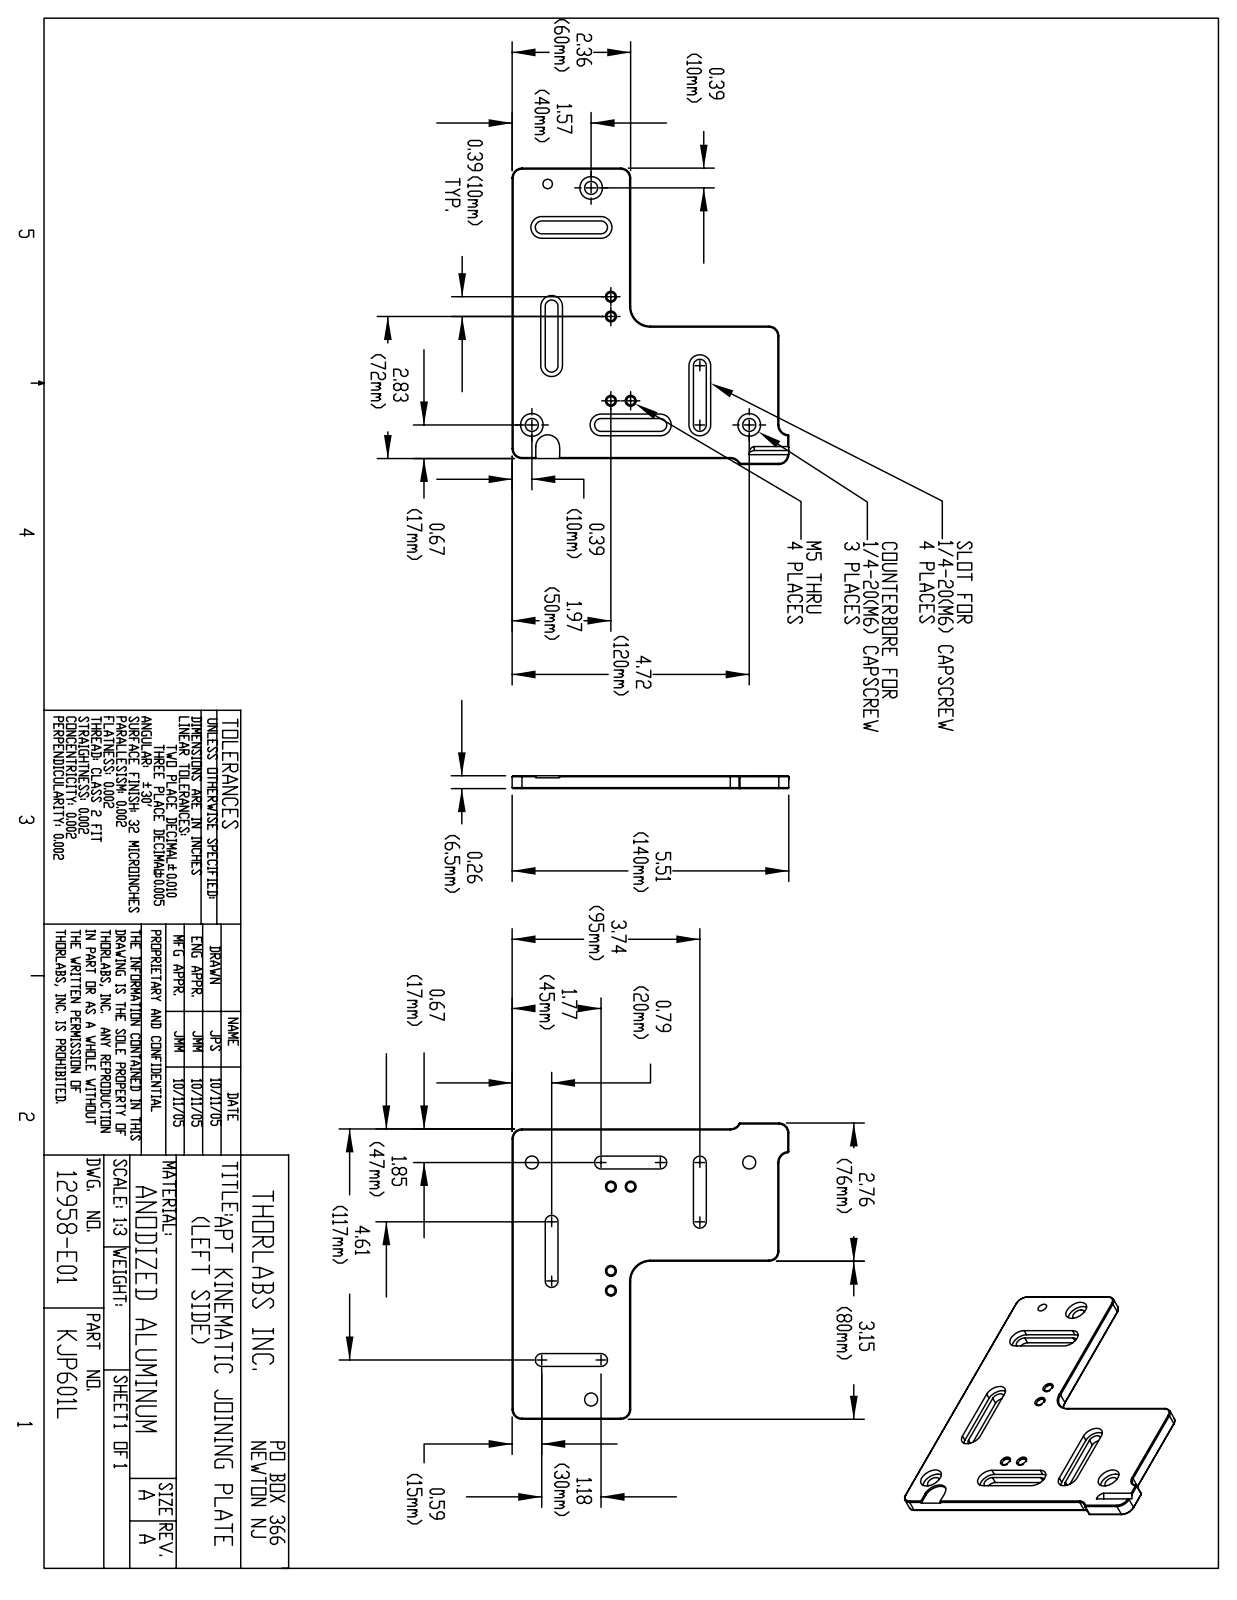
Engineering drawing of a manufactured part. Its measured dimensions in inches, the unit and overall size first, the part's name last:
Units: inches
Overall size (bounding box): 5.906 × 5.512 × 0.256
Round holes (diameter × count): ⌀0.165 ×4, ⌀0.26 ×3, ⌀0.453 ×3
Partial cylindrical surfaces — rounded edges, fillets, slot ends (radius × count): R0.02 ×18, R0.128 ×8, R0.217 ×8, R0.197 ×7, R0.098 ×1, R0.236 ×1, R0.394 ×1
Main face-to-face distances: 0.256, 0.118, 0.138, 0.089, 0.344, 2.953, 3.937, 0.433, 2.362, 2.638
Hole centre spacings: 0.394, 1.646, 1.681, 1.727, 2.026, 2.075, 2.112, 2.205
Bodies: 0 solids, 146 faces (38 planar, 70 cylindrical, 38 other)
Part name (STEP PRODUCT): 12958-E0W
STEP written by: SolidWorks 2007 (AUTOMOTIVE_DESIGN)
